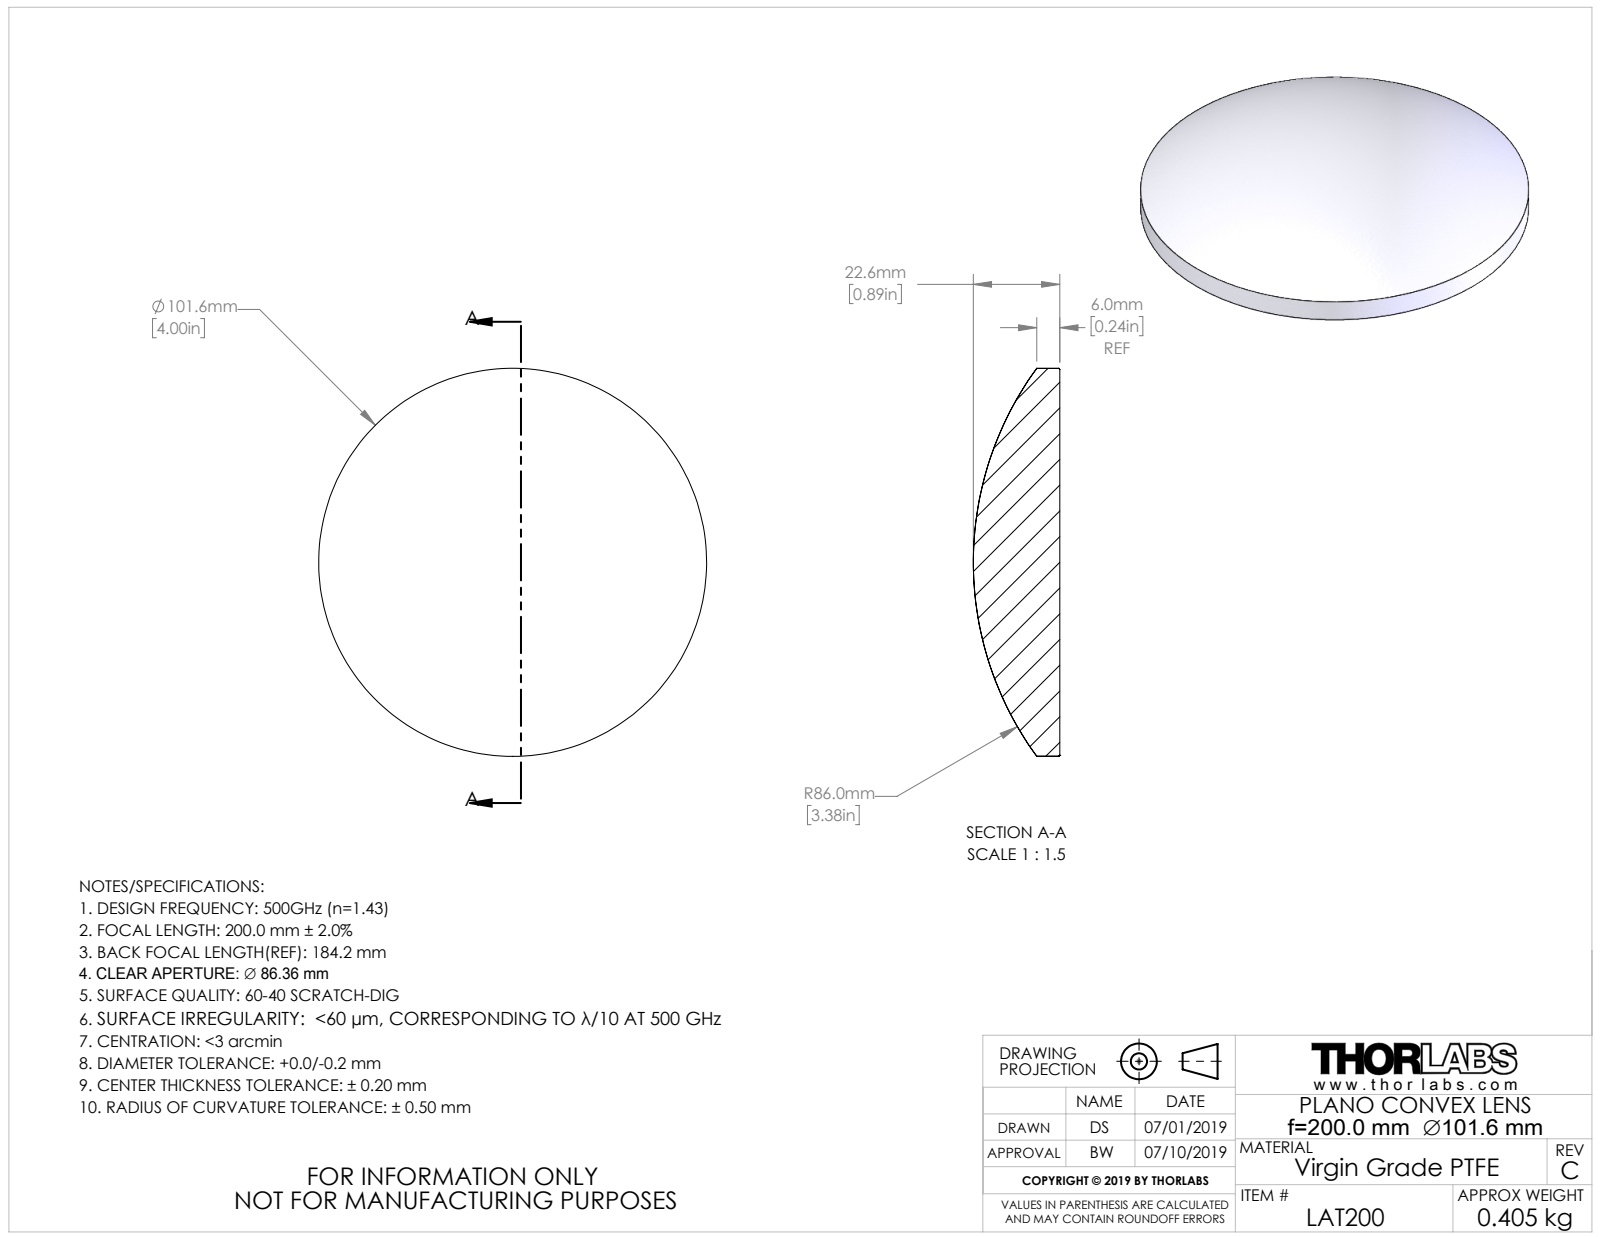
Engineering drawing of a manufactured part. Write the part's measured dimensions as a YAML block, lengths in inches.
part_name: "TTN041009-E0W"
step_written_by: "SolidWorks 2018 (CONFIG_CONTROL_DESIGN)"
units: inches
bodies: {solids: 1, faces: 7, planar: 1, cylindrical: 2, other: 4}
overall_size: [4, 4, 0.891]
volume: 7.24
surface_area: 29.39
round_bosses_or_shafts:
  - {diameter: 4, count: 1}
